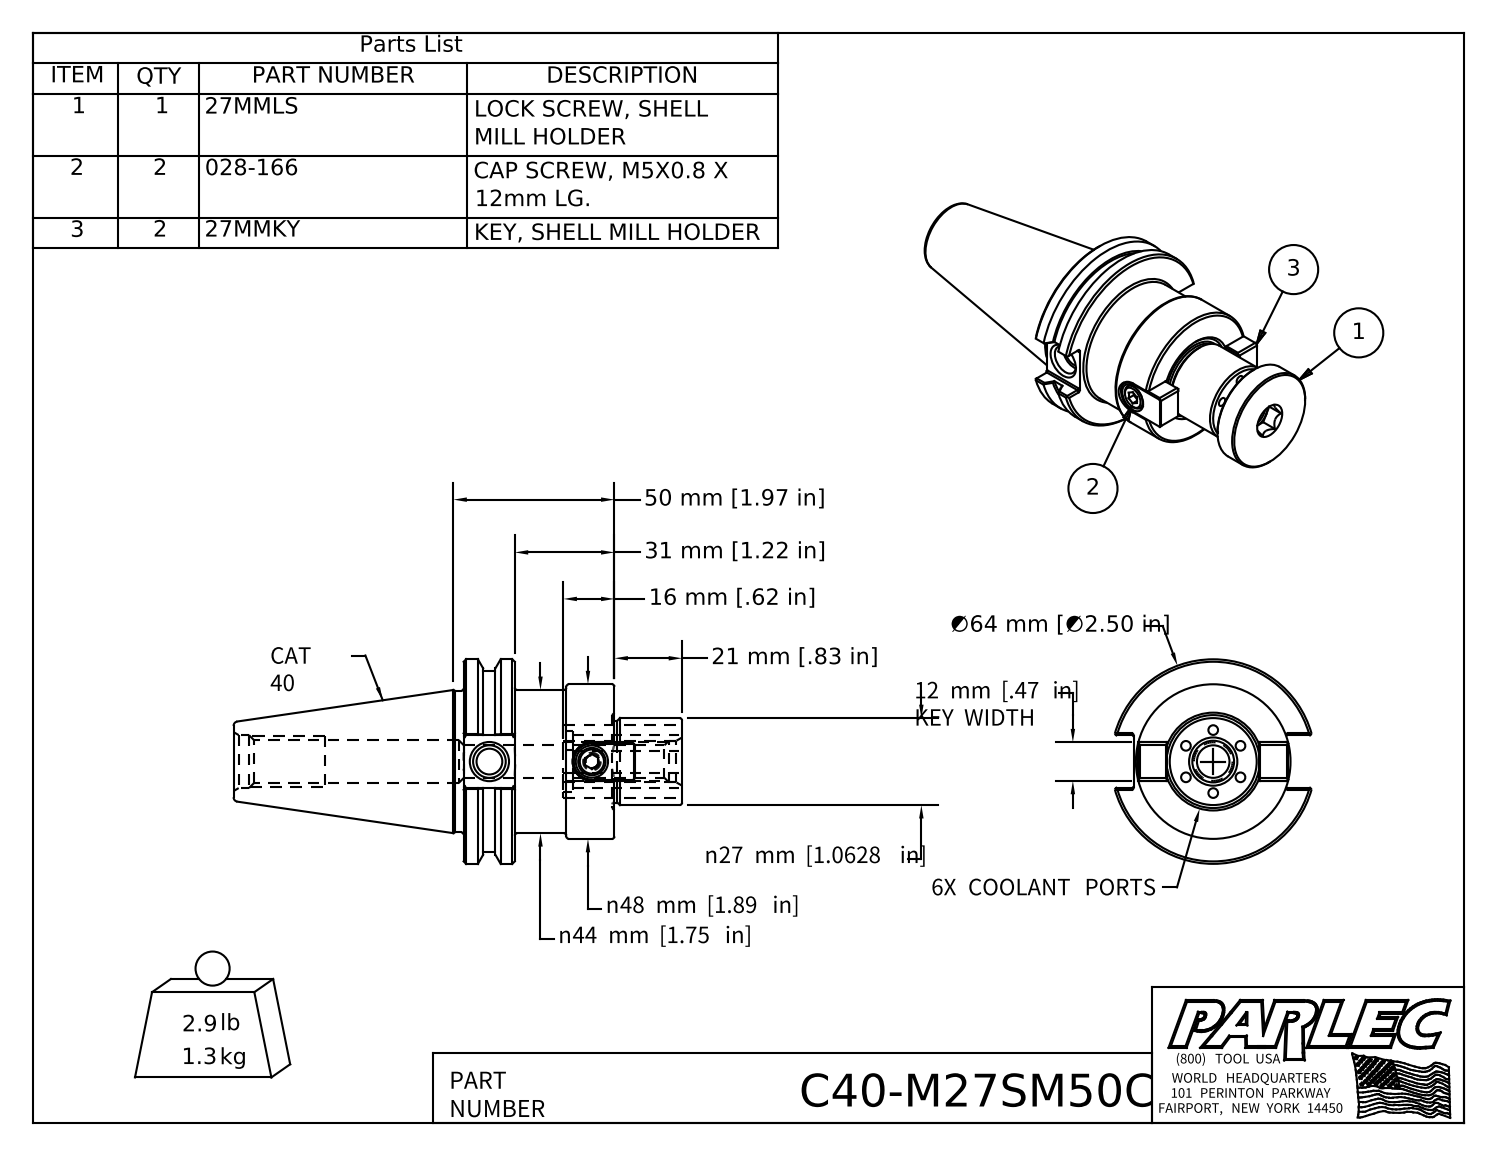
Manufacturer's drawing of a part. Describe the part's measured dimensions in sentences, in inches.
The part is named "C40-M27SM50C; 27MMKY; 028-166; 27MMLS". Its 3-D file was written by "Autodesk Inventor 2022 (AUTOMOTIVE_DESIGN)". It is 6 solids with 216 faces: 106 planar, 59 cylindrical and 51 other. Overall it measures 6.047 by 2.5 by 2.406 inches. Its volume is 10.3 cubic inches and its surface area 59.33 square inches. Round holes: 6 of diameter 0.118, 1 of diameter 0.163, 1 of diameter 0.217, 1 of diameter 0.315, 1 of diameter 0.394, 1 of diameter 0.394, 1 of diameter 0.398, 1 of diameter 0.399, 1 of diameter 0.51, 1 of diameter 0.527, 1 of diameter 0.648. Round bosses or shafts: 1 of diameter 2.5, 1 of diameter 2.219, 1 of diameter 1.89, 1 of diameter 1.75, 1 of diameter 1.73, 1 of diameter 1.378, 1 of diameter 1.063, 1 of diameter 1.003. Partial cylindrical surfaces (rounded edges, fillets, slot ends): 12 of radius 0.02, 1 of radius 0.235, 1 of radius 0.236, 1 of radius 0.375. The main face-to-face distances are 0.625, 2.61, 3.235, 1.844, 1.219, 1.392, 0.315, 2.92, 2.295, 1.077. The hole center spacings are 0.385, 0.667, 0.77, 1.252.
